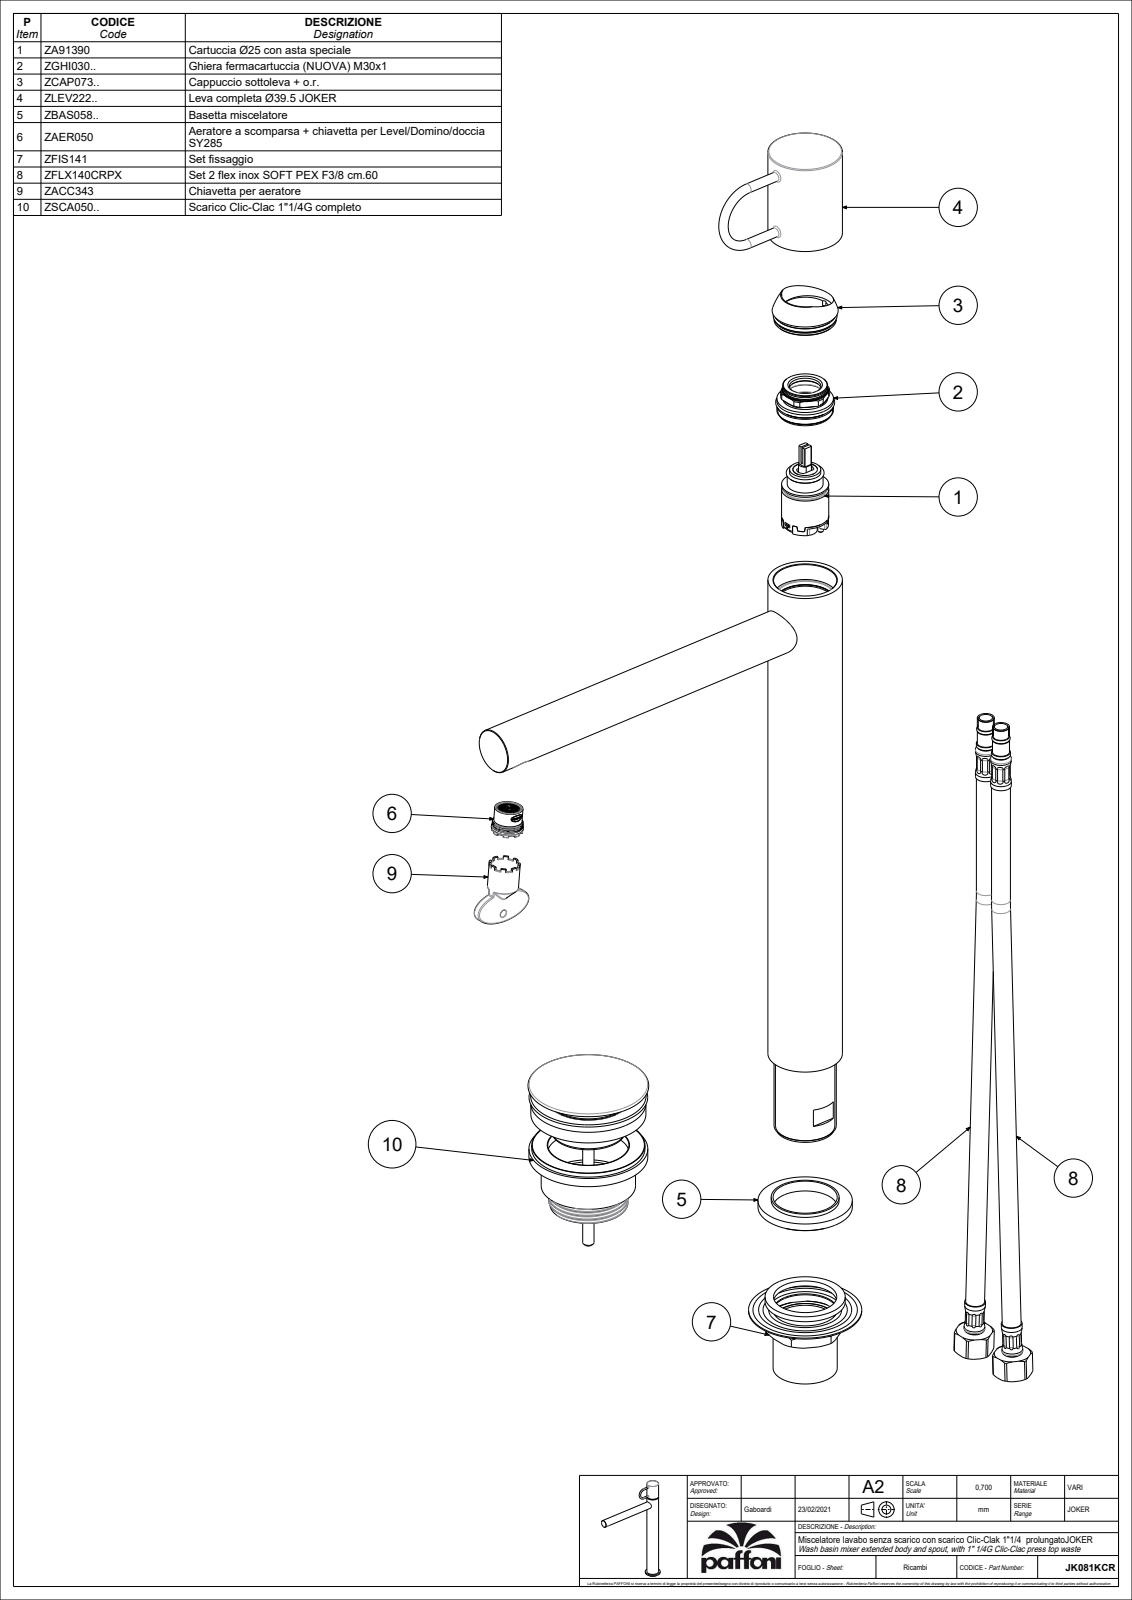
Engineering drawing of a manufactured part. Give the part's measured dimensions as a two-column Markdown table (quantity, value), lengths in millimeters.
| quantity | value |
| --- | --- |
| part name | JK081CR |
| STEP written by | CREO PARAMETRIC BY PTC INC, 2020044 (CONFIG_CONTROL_DESIGN) |
| units | millimeters |
| bodies | 1 solid, 2925 faces (1934 planar, 625 cylindrical, 366 other) |
| overall size | 346.85 × 240.9 × 50 |
| volume | 223 043 mm³ |
| surface area | 152 619 mm² |
| round holes (diameter × count) | 6.5 × 4, 7 × 3, 3.2 × 2, 5 × 2, 9.4 × 2, 11 × 2, 3 × 1, 4.2 × 1, 5.5 × 1, 8 × 1, 12.15 × 1, 12.45 × 1 |
| round bosses / shafts (diameter × count) | 10 × 4, 0.9 × 3, 11 × 2, 9 × 2, 5 × 2, 4 × 2, 50 × 1, 43 × 1 |
| partial cylindrical surfaces (radius × count) | 0.12 × 51, 3 × 28, 0.5 × 18, 0.2 × 8, 0.6 × 5, 1 × 5, 2 × 4, 3.5 × 3 |
| main face-to-face distances | 2, 4, 344.5, 340.5, 50.5, 6.5, 243.5, 239.5, 101, 14.8 |
| hole center spacings | 1.5, 6.72, 7.85, 8.92, 8.94, 9.33, 11, 15.46 |
